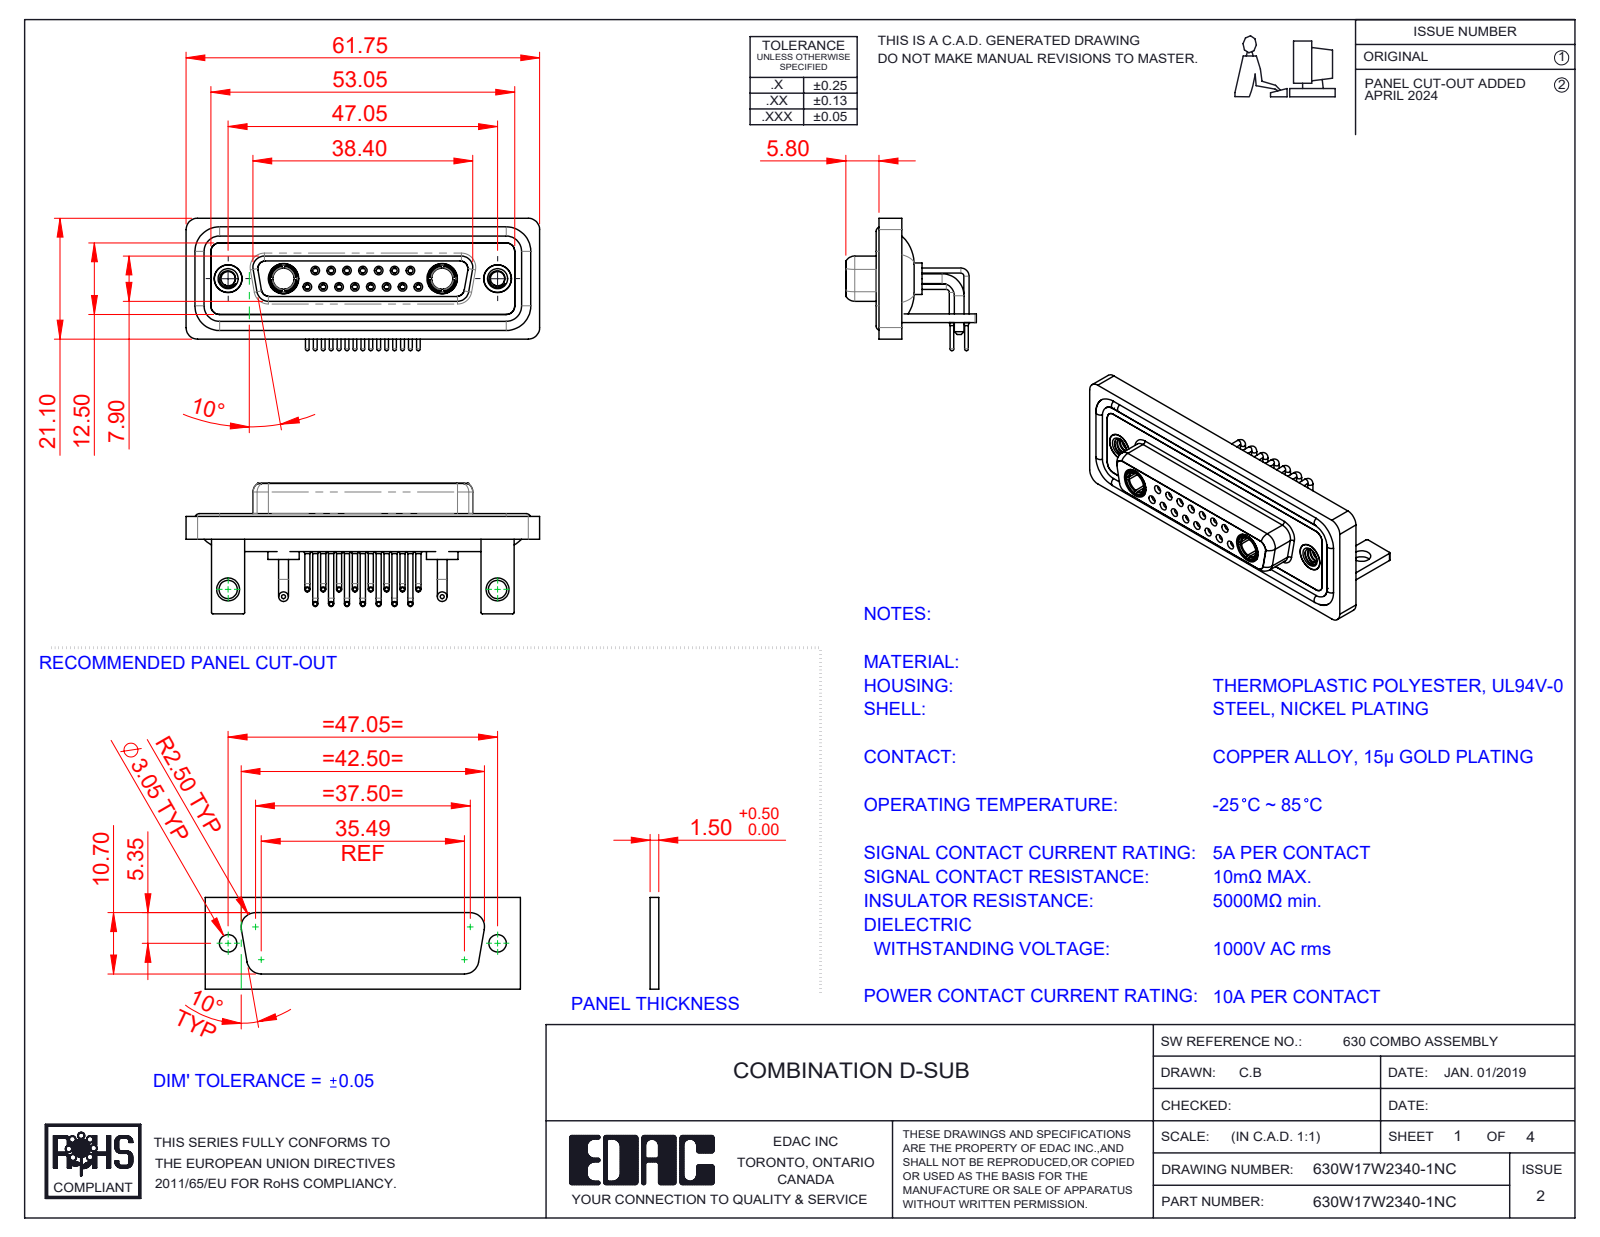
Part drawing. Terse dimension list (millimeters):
name: 630Combo Housing_17W2; Power Socket_10A RA; 630Combo Stabilizer Bracket_50 Contacts; 630W17W2340-1NC (+6 more)
written by: SolidWorks 2023 (CONFIG_CONTROL_DESIGN)
unit: mm
bodies: 28 solids, 1379 faces (408 planar, 605 cylindrical, 366 other)
size: 61.75 × 23.12 × 22.8
volume: 8 730 mm³; area: 15 167 mm²
holes: 15× ⌀0.9, 15× ⌀1.1, 15× ⌀1.5, 15× ⌀2, 8× ⌀1.6, 7× ⌀1.7, 4× ⌀4.85, 2× ⌀2.5, 2× ⌀3.2, 2× ⌀3.7, 2× ⌀4, 2× ⌀4.05
bosses: 15× ⌀0.9, 15× ⌀0.65, 11× ⌀1.6, 4× ⌀1.7, 2× ⌀5.5, 2× ⌀5.2, 2× ⌀4.96, 2× ⌀4.95
rounds: 19× R2, 18× R1.5, 16× R0.25, 8× R1.35, 8× R1.6, 5× R0.5, 4× R0.6, 4× R0.65
face distances: 0.4, 1.8, 2.9, 3.7, 1.5, 4.1, 1.1, 1.4, 1.6, 3.1
hole spacings: 3.16, 2.77, 5.54, 8.31, 5.04, 7.49, 11.08, 5.03
